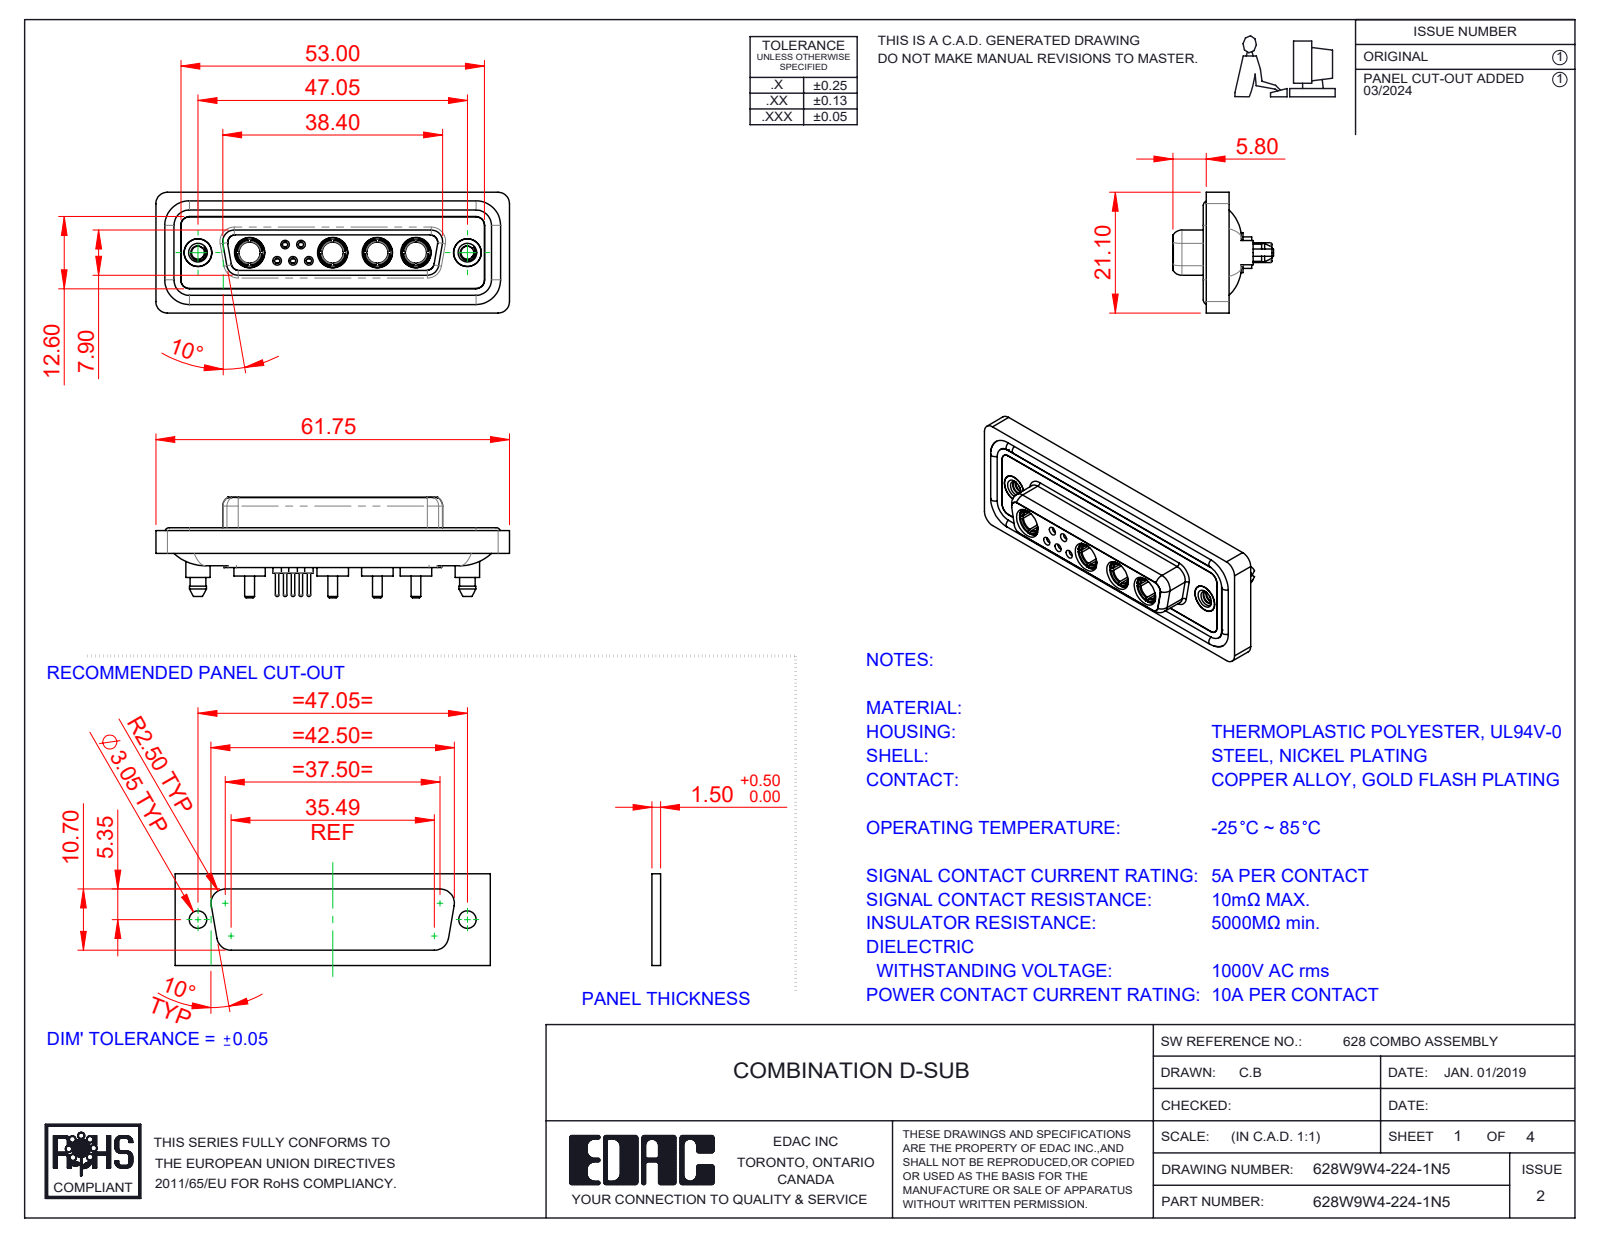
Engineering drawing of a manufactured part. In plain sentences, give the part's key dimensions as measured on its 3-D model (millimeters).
The part is named "628Combo Shell Rear_25 Contacts; 628Combo Housing_9W4; Power Socket_10A S; 628W9W4-224-1N5 (+5 more)". Its 3-D file was written by "SolidWorks 2023 (CONFIG_CONTROL_DESIGN)". It is 20 solids with 1007 faces: 312 planar, 407 cylindrical and 288 other. Overall it measures 61.75 by 21.1 by 17.55 millimeters. Its volume is 8 298 cubic millimeters and its surface area 13 844 square millimeters. Round holes: 6 of diameter 4.85, 5 of diameter 0.9, 5 of diameter 1.1, 5 of diameter 1.5, 5 of diameter 2, 4 of diameter 3.7, 4 of diameter 5.3, 3 of diameter 1.6, 2 of diameter 1.7, 2 of diameter 2.26, 2 of diameter 4, 2 of diameter 4.05. Round bosses or shafts: 6 of diameter 1.6, 5 of diameter 2.2, 5 of diameter 0.6, 4 of diameter 5.5, 4 of diameter 5.2, 4 of diameter 4.96, 4 of diameter 4.75, 4 of diameter 3.75. Partial cylindrical surfaces (rounded edges, fillets, slot ends): 24 of radius 1.5, 18 of radius 2, 10 of radius 1.6, 8 of radius 1.35, 4 of radius 0.25, 4 of radius 0.5, 4 of radius 0.6, 4 of radius 0.65. The main face-to-face distances are 0.4, 1.8, 7.45, 5.65, 0.5, 7.05, 6.6, 1.6, 1.1, 2.9. The hole center spacings are 3.16, 2.77, 5.03, 2.76, 4.4, 5.02, 5.54, 5.73.
